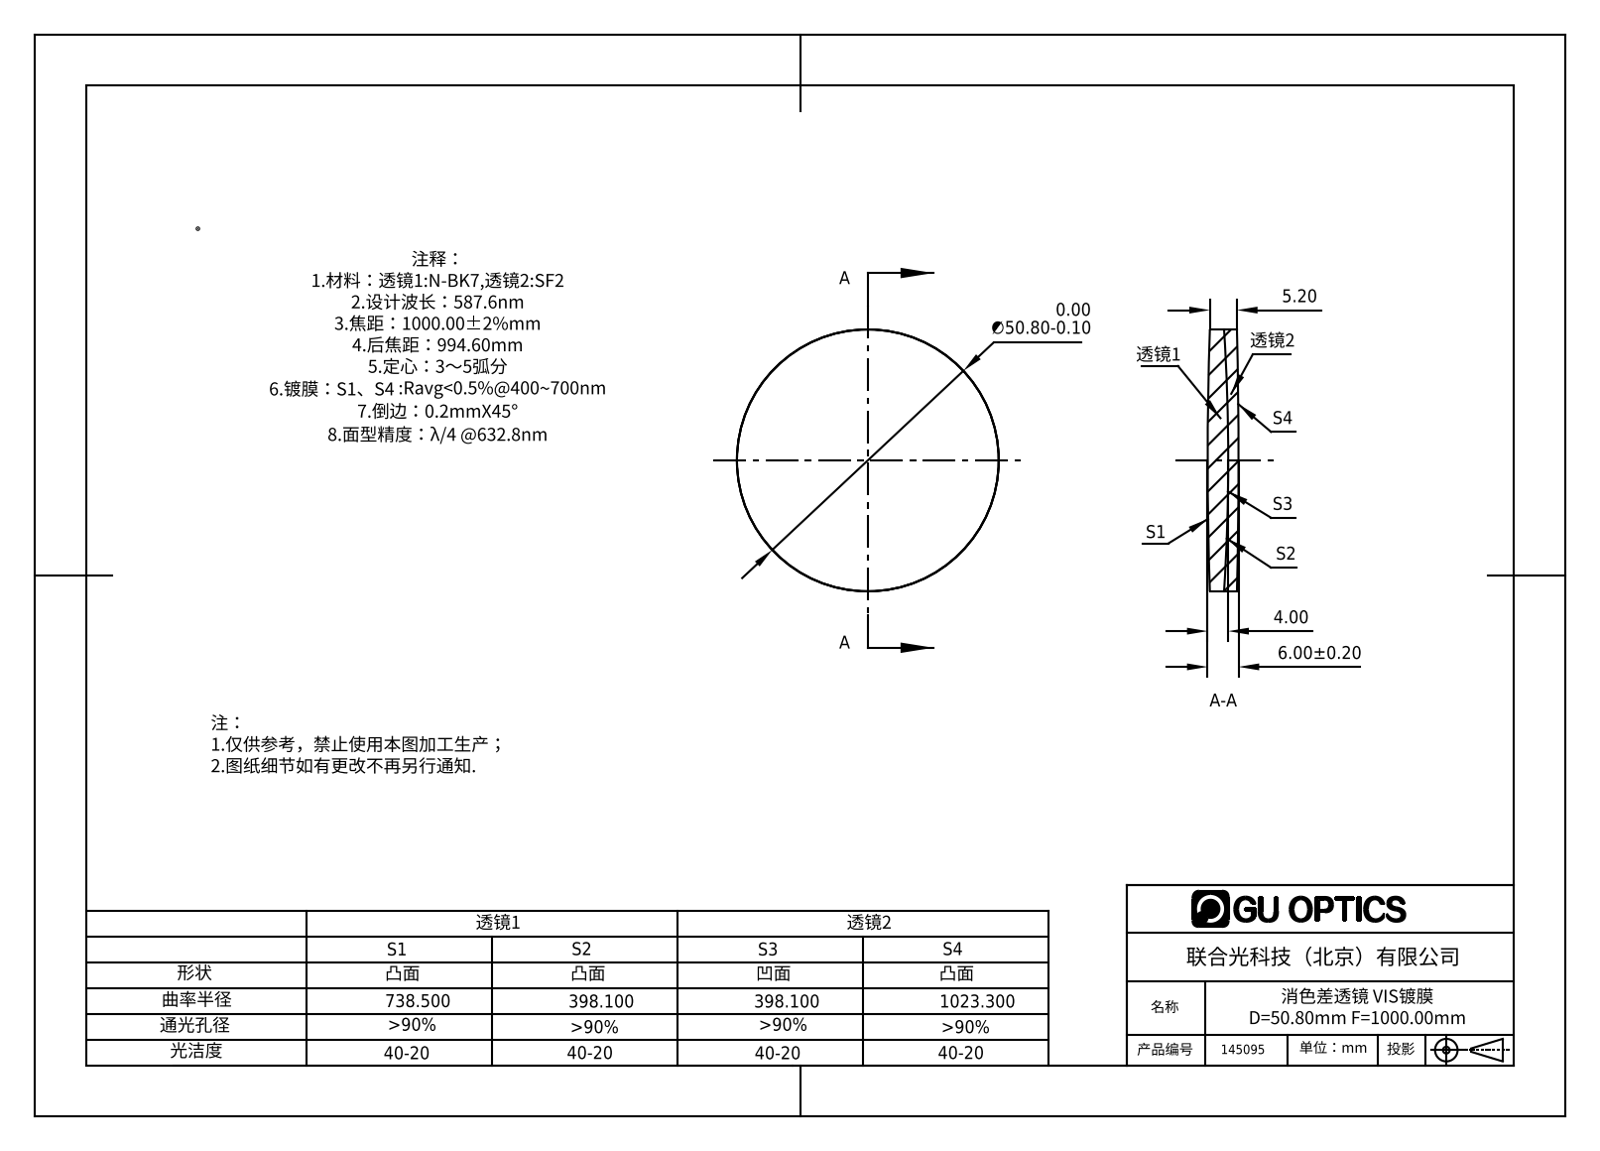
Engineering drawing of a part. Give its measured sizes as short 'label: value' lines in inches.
name: 145095
written by: SolidWorks 2016 (AUTOMOTIVE_DESIGN)
unit: in
bodies: 2 solids, 12 faces (0 planar, 4 cylindrical, 8 other)
size: 2 × 2 × 0.236
volume: 0.696 in³; area: 13.87 in²
bosses: 1× ⌀2
